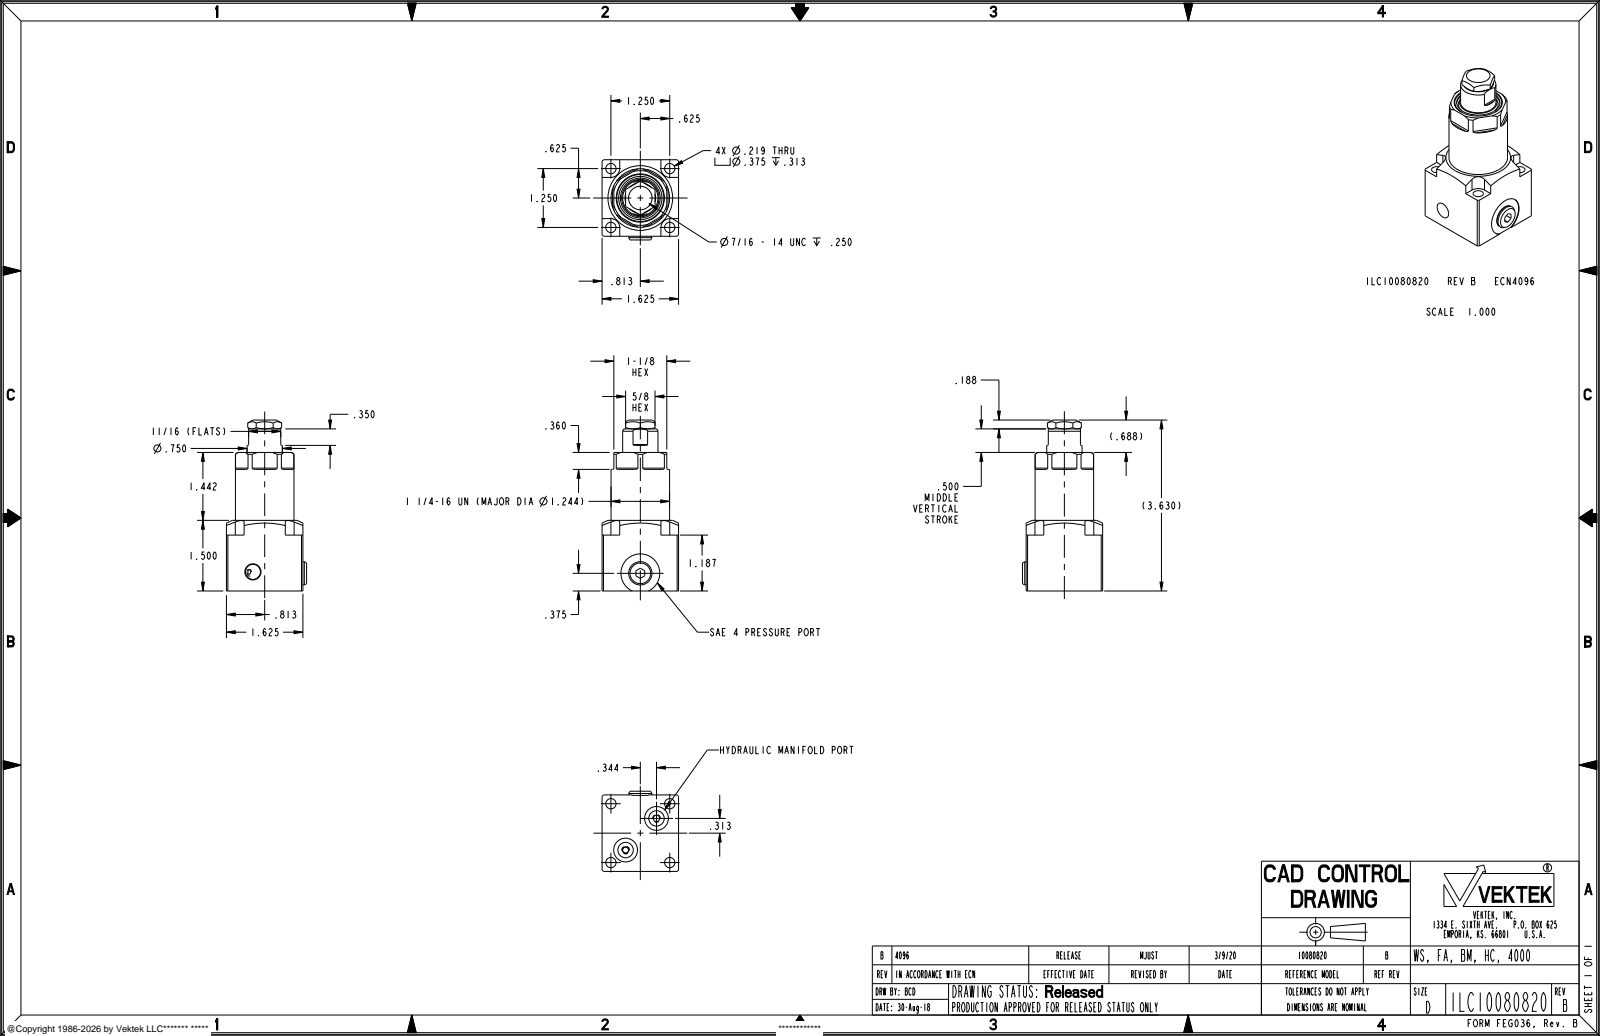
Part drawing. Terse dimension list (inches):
name: ILC10080820
written by: PRO/ENGINEER BY PARAMETRIC TECHNOLOGY CORPORATION, 2017170 (AUTOMOTIVE_DESIGN)
unit: in
bodies: 1 solid, 171 faces (70 planar, 57 cylindrical, 44 other)
size: 3.63 × 1.704 × 1.625
volume: 5.4 in³; area: 28.8 in²
holes: 4× ⌀0.219, 2× ⌀0.136, 2× ⌀0.164, 2× ⌀0.328, 2× ⌀0.505, 1× ⌀0.125, 1× ⌀0.368, 1× ⌀0.392, 1× ⌀0.825, 1× ⌀0.92
bosses: 2× ⌀0.437, 1× ⌀1.244, 1× ⌀1, 1× ⌀0.75, 1× ⌀0.438
rounds: 6× R0.027, 4× R0.187, 2× R0.018
face distances: 1.625, 1.625, 0.25, 1.125, 1.187, 1.615, 1.375, 0.875, 1.5, 0.313
hole spacings: 0.884, 1.25, 1.769, 0.41, 0.42, 0.465, 0.476, 0.94
